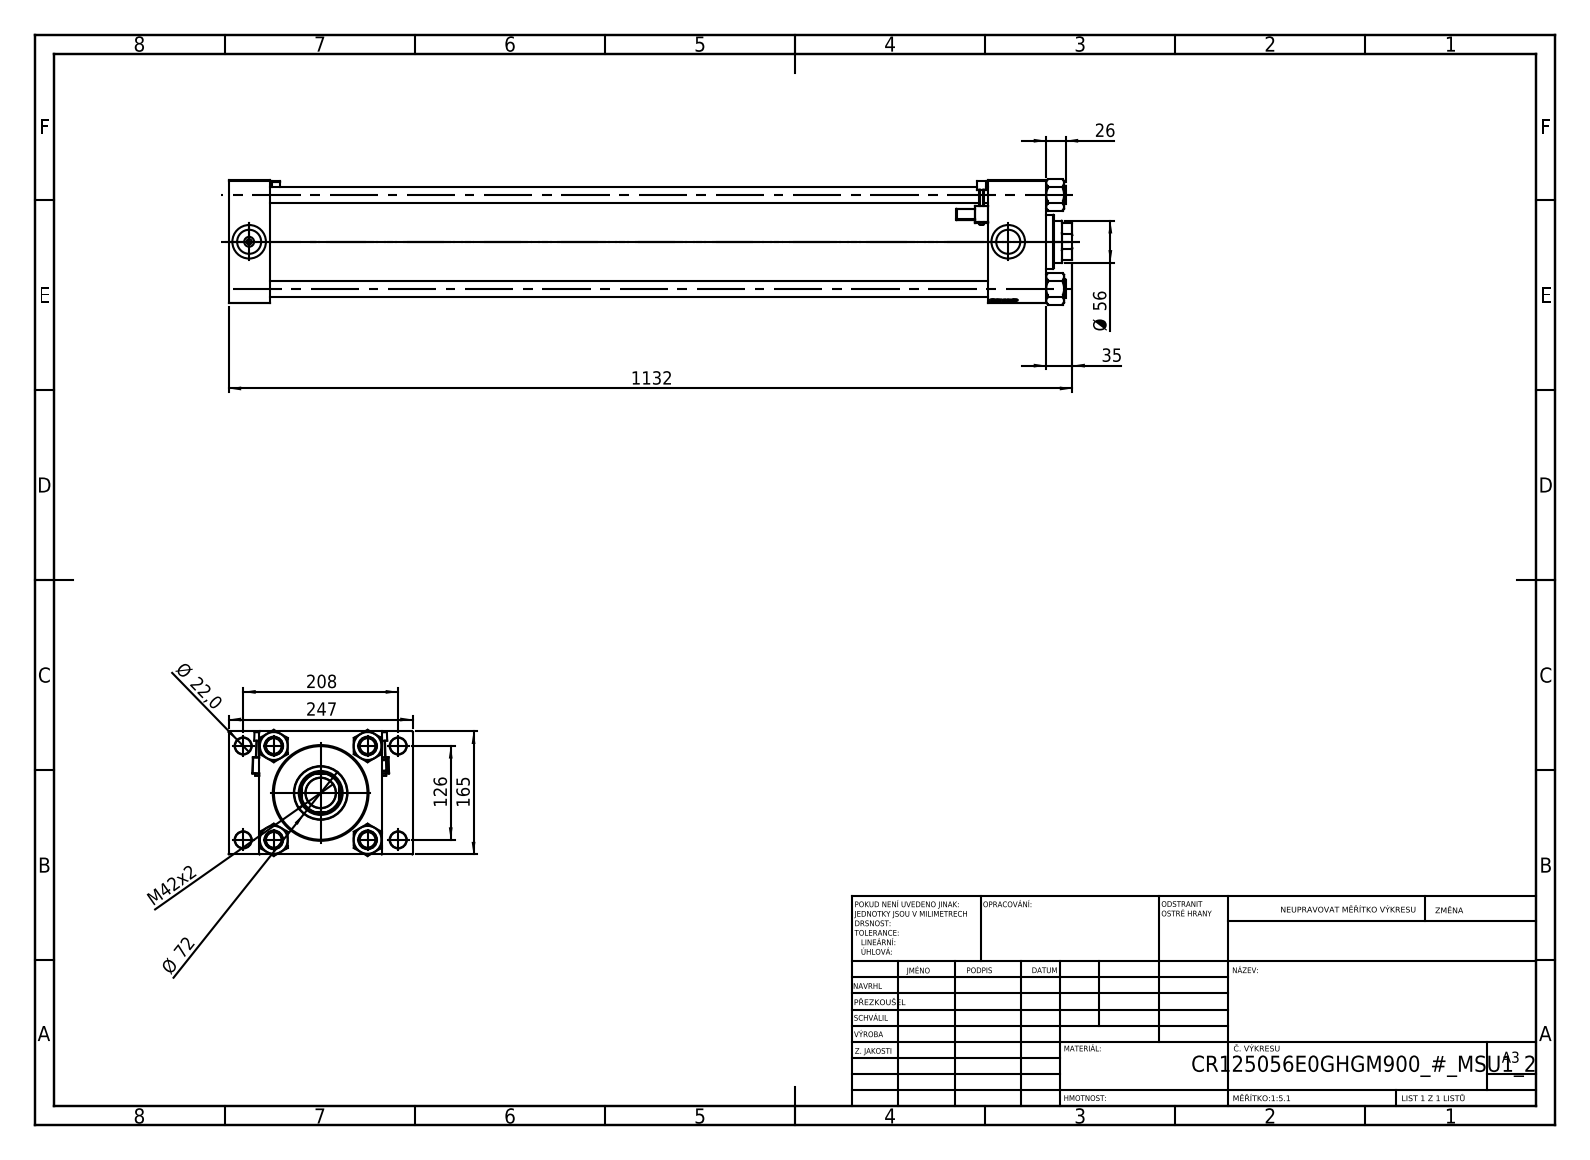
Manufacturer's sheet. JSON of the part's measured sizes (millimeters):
{"part_name": "V215CR_VCP_E; NUT_M5_E; V215_VC_A; V215CR_MSU (+2 more)", "step_written_by": "SolidWorks 2019 (CONFIG_CONTROL_DESIGN)", "units": "millimeters", "bodies": {"solids": 13, "faces": 1338, "planar": 604, "cylindrical": 146, "other": 588}, "overall_size": [1132, 247, 169.14], "volume_mm3": 9783000, "surface_area_mm2": 1691000, "round_holes": [[22, 8], [7, 2], [32.24, 2], [45, 2], [40.5, 1], [56, 1], [59, 1], [96, 1], [125, 1], [125.5, 1]], "round_bosses_or_shafts": [[25, 4], [6, 2], [131, 1], [72, 1]], "partial_cylinders_radius": [[0.5, 48], [1, 2], [2.5, 2], [4, 2], [27, 1]], "face_to_face_distances": [165, 55, 1097, 1042, 1019, 964, 78, 41, 206, 1068.3], "hole_center_spacings": [41.05, 89.02, 121.59, 125.9, 132.47, 166.95, 209.13, 126]}
